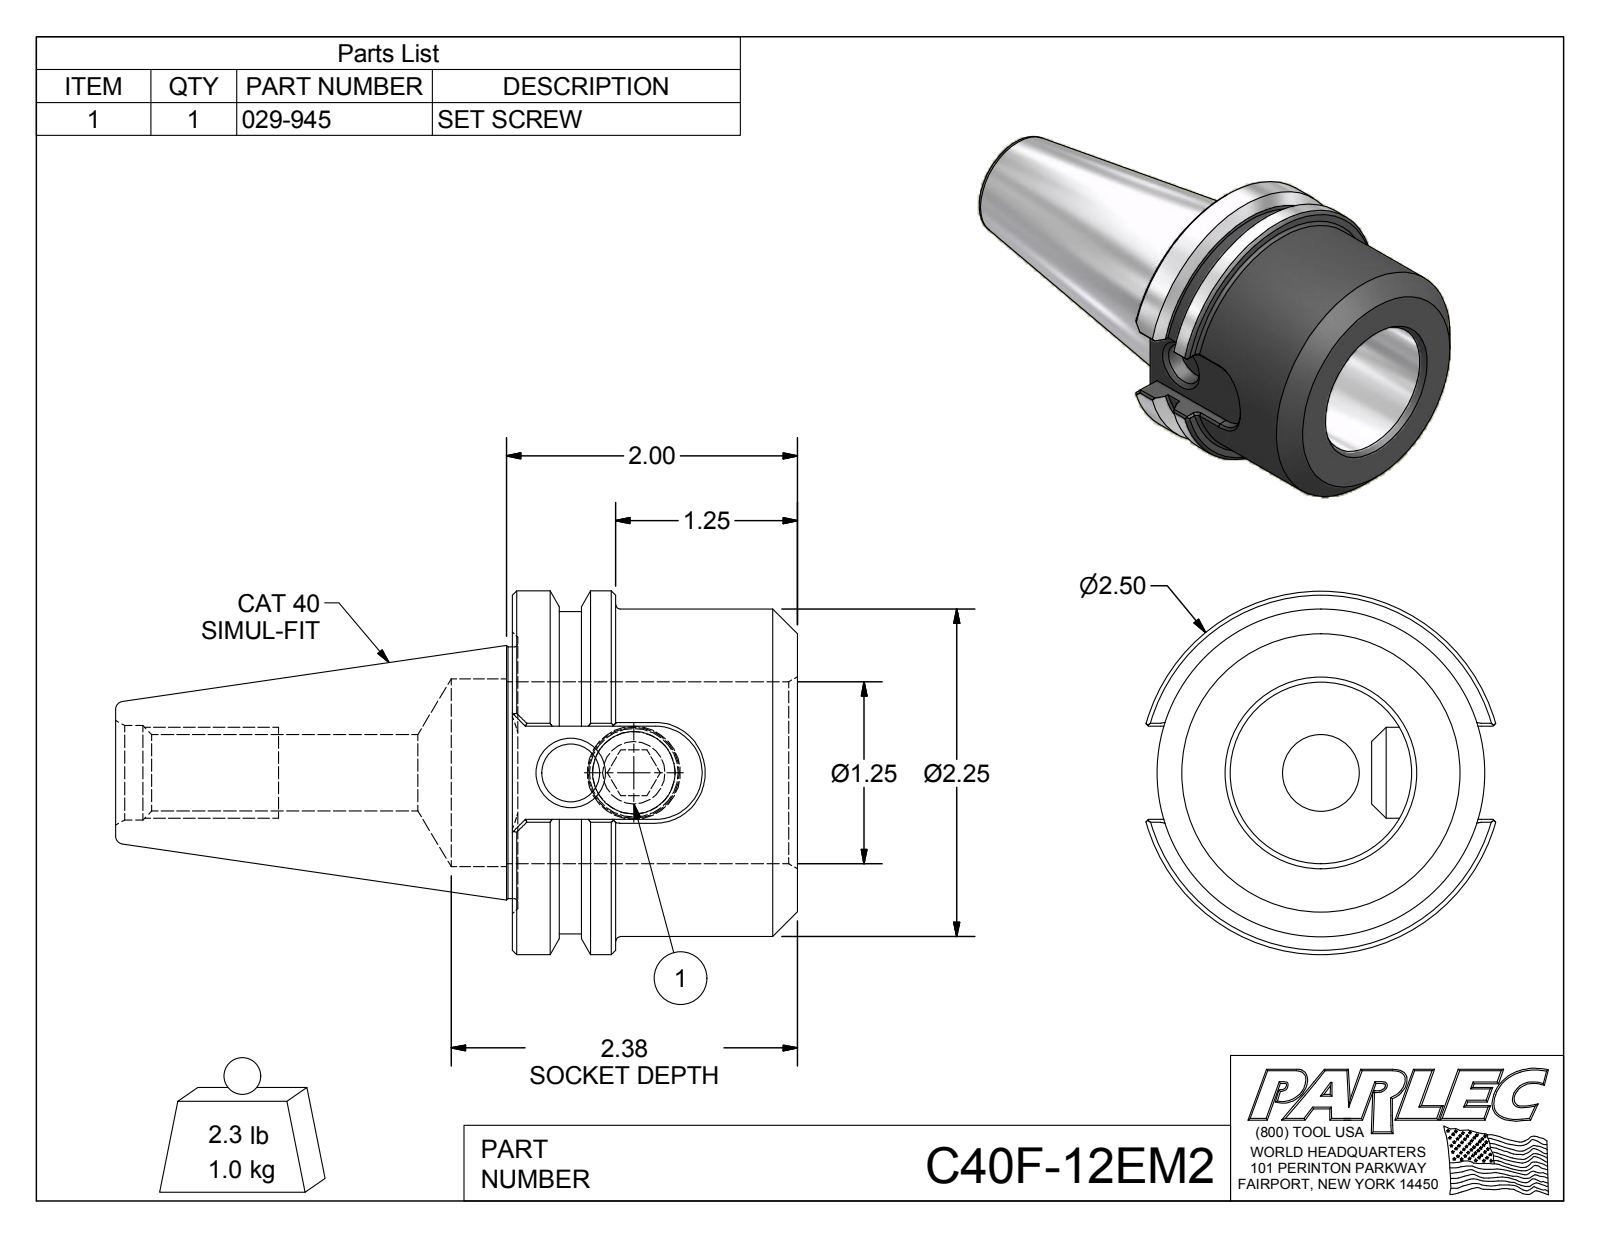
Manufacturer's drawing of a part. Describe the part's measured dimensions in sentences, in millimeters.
The part is named "C40F-12EM2; C40F-12EM2-1; 029-945". Its 3-D file was written by "Autodesk Inventor 2012 (AUTOMOTIVE_DESIGN)". It is 2 solids with 99 faces: 40 planar, 17 cylindrical and 42 other. Overall it measures 119.1 by 63.5 by 61.1 millimeters. Its volume is 135 700 cubic millimeters and its surface area 32 000 square millimeters. Round holes: 1 of diameter 10.1, 1 of diameter 13.4, 1 of diameter 14.4, 1 of diameter 16.5, 1 of diameter 31.8, 1 of diameter 32.8. Round bosses or shafts: 1 of diameter 63.5, 1 of diameter 57.2, 1 of diameter 56.3, 1 of diameter 43.9, 1 of diameter 15.9. Partial cylindrical surfaces (rounded edges, fillets, slot ends): 1 of radius 8.1. The main face-to-face distances are 49.8, 47.2, 18.1, 31.8, 16.3, 0.9, 17.1, 48.9, 1, 46.3. The hole center spacings are 11.
